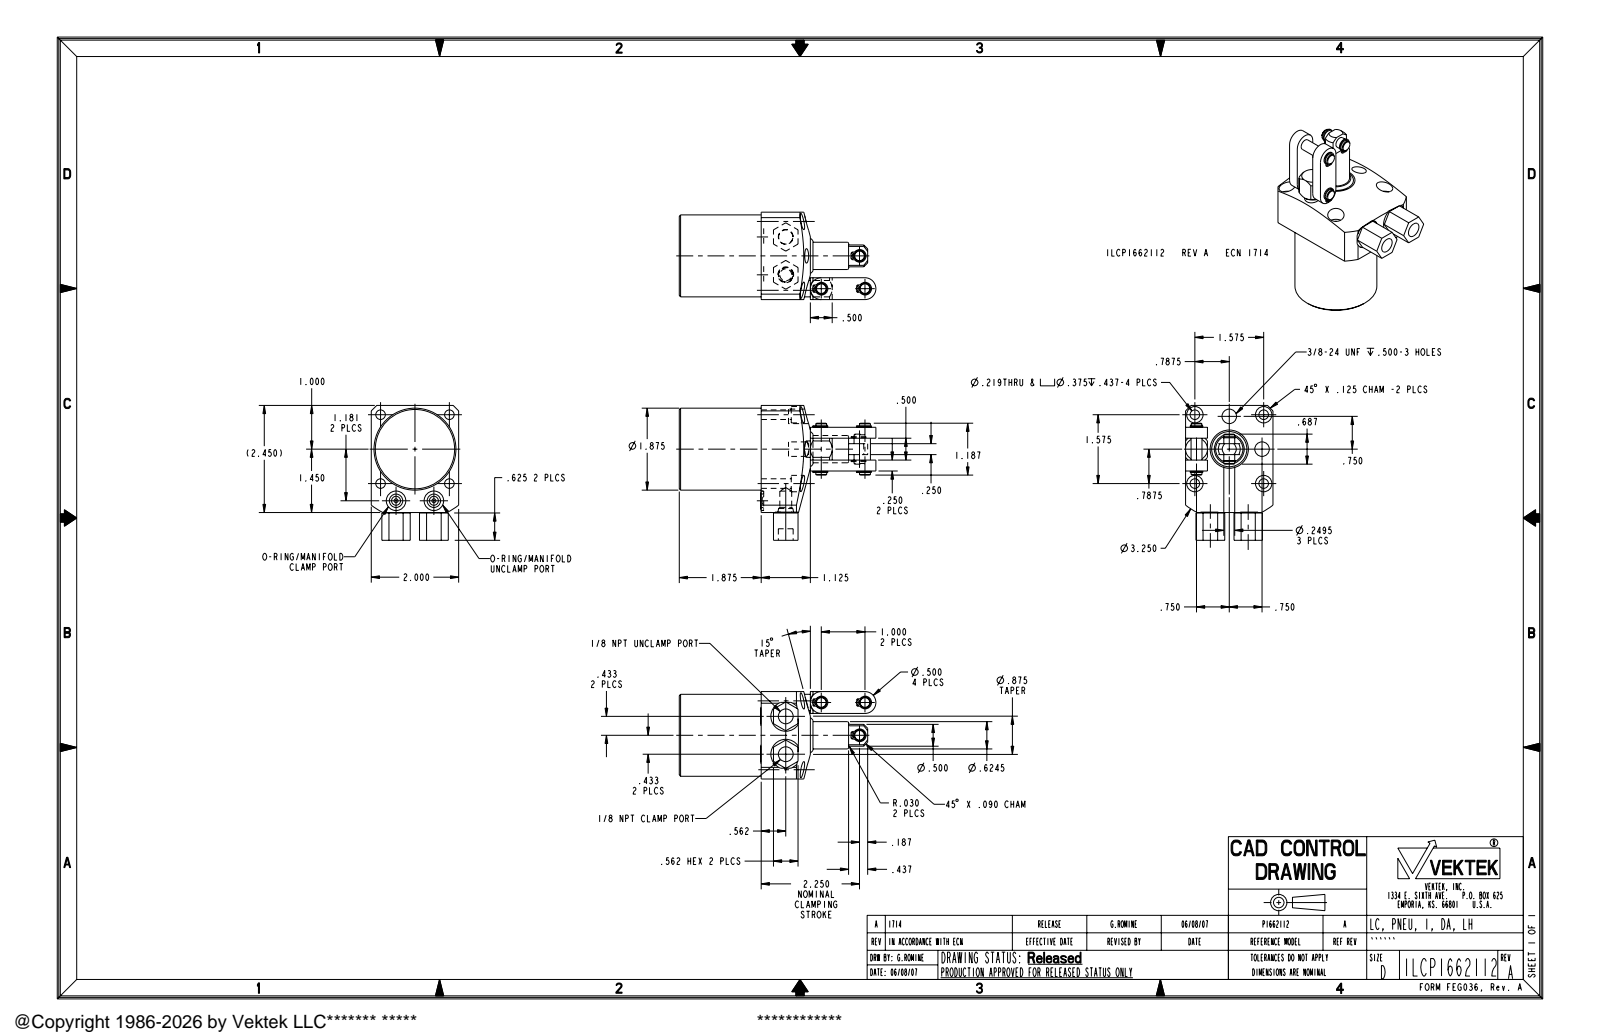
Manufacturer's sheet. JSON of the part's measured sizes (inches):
{"part_name": "ILCP1662112", "step_written_by": "PRO/ENGINEER BY PARAMETRIC TECHNOLOGY CORPORATION, 2005180 (AUTOMOTIVE_DESIGN_CC2)", "units": "inches", "bodies": {"solids": 3, "faces": 304, "planar": 120, "cylindrical": 132, "other": 52}, "overall_size": [4.5, 3.085, 2], "volume_in3": 10.85, "surface_area_in2": 46.73, "round_holes": [[0.041, 6], [0.219, 4], [0.375, 4], [0.272, 2], [0.332, 2], [0.339, 2], [0.447, 2]], "round_bosses_or_shafts": [[0.25, 3], [0.312, 2], [1.875, 1], [0.624, 1], [0.375, 1]], "partial_cylinders_radius": [[0.041, 12], [0.145, 3], [0.25, 3], [0.341, 2], [0.313, 1], [1.625, 1]], "face_to_face_distances": [2, 0.5, 1.875, 0.75, 0.25, 1.5, 0.562, 1, 2.45, 1.95], "hole_center_spacings": [0.788, 1.575, 1.727, 0.098, 0.53, 0.76, 0.866, 1]}
